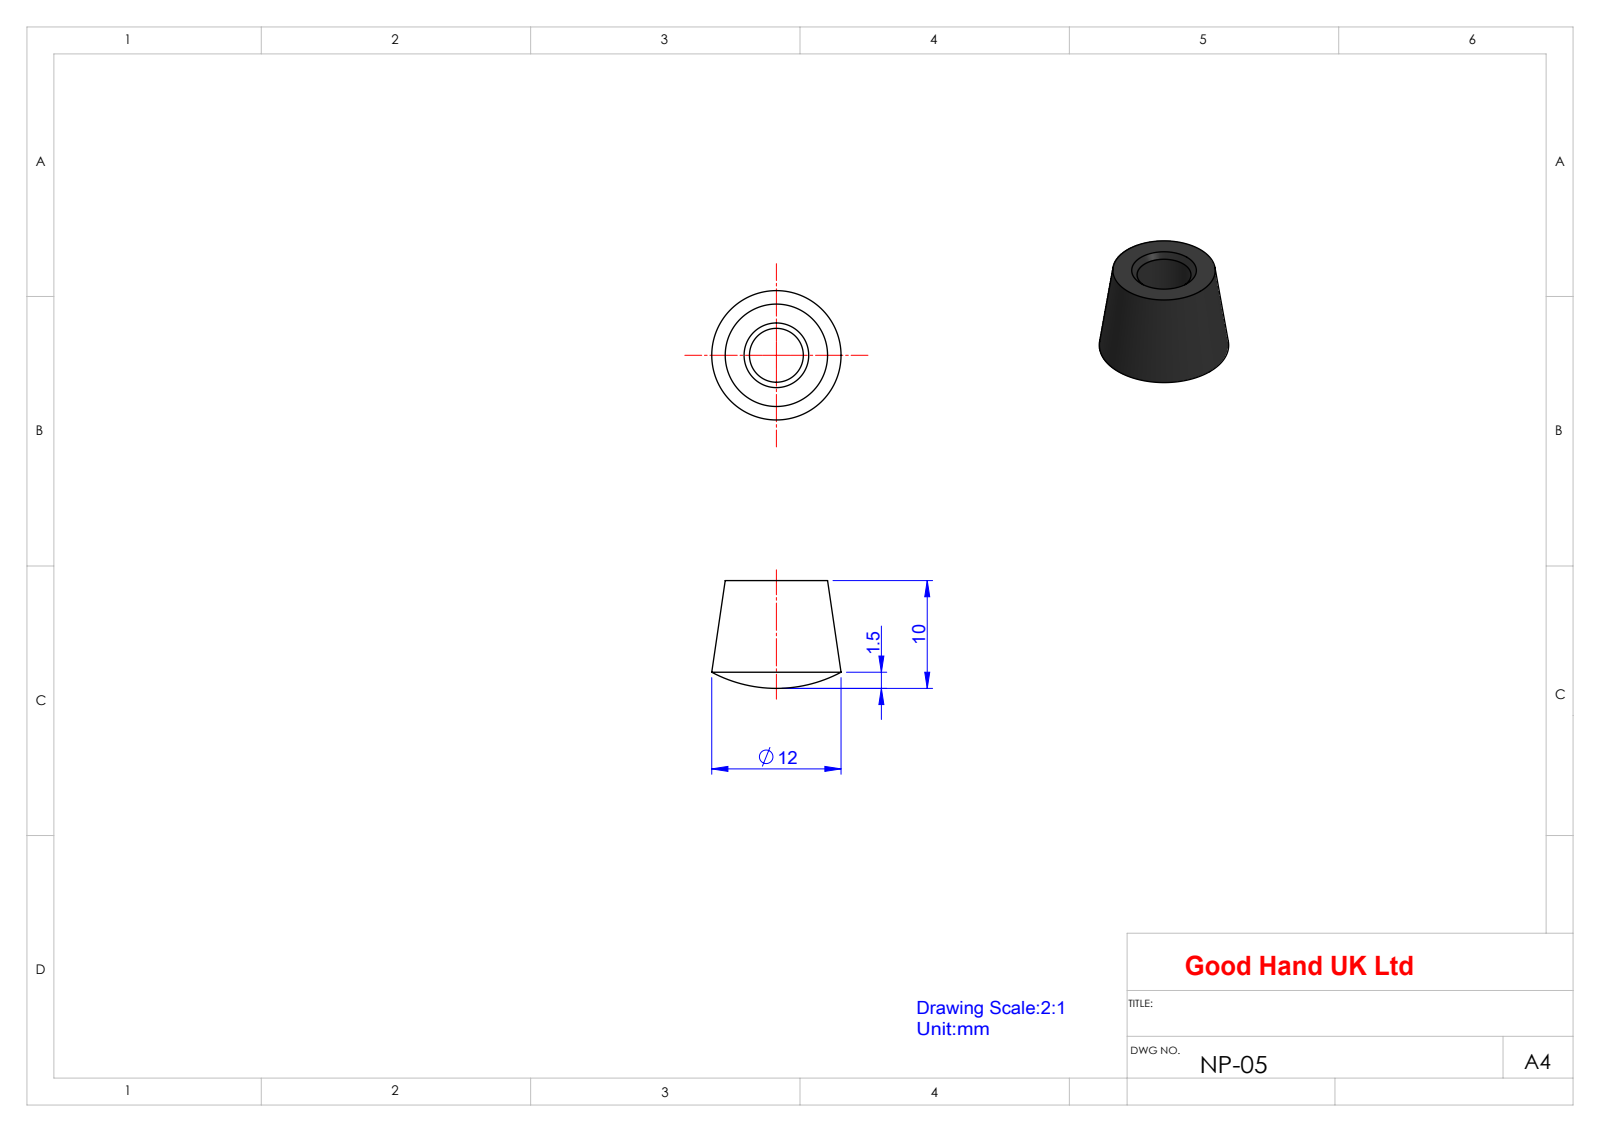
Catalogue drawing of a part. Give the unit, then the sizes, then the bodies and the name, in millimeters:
Units: millimetres
Overall size (bounding box): 12 × 12 × 10
Round holes (diameter × count): ⌀5 ×1
Main face-to-face distances: 7
Volume: 722 mm³ · Surface area: 587 mm²
Bodies: 1 solid, 10 faces (2 planar, 2 cylindrical, 6 other)
Part name (STEP PRODUCT): NP-05
STEP written by: SolidWorks 2016 (AUTOMOTIVE_DESIGN)
